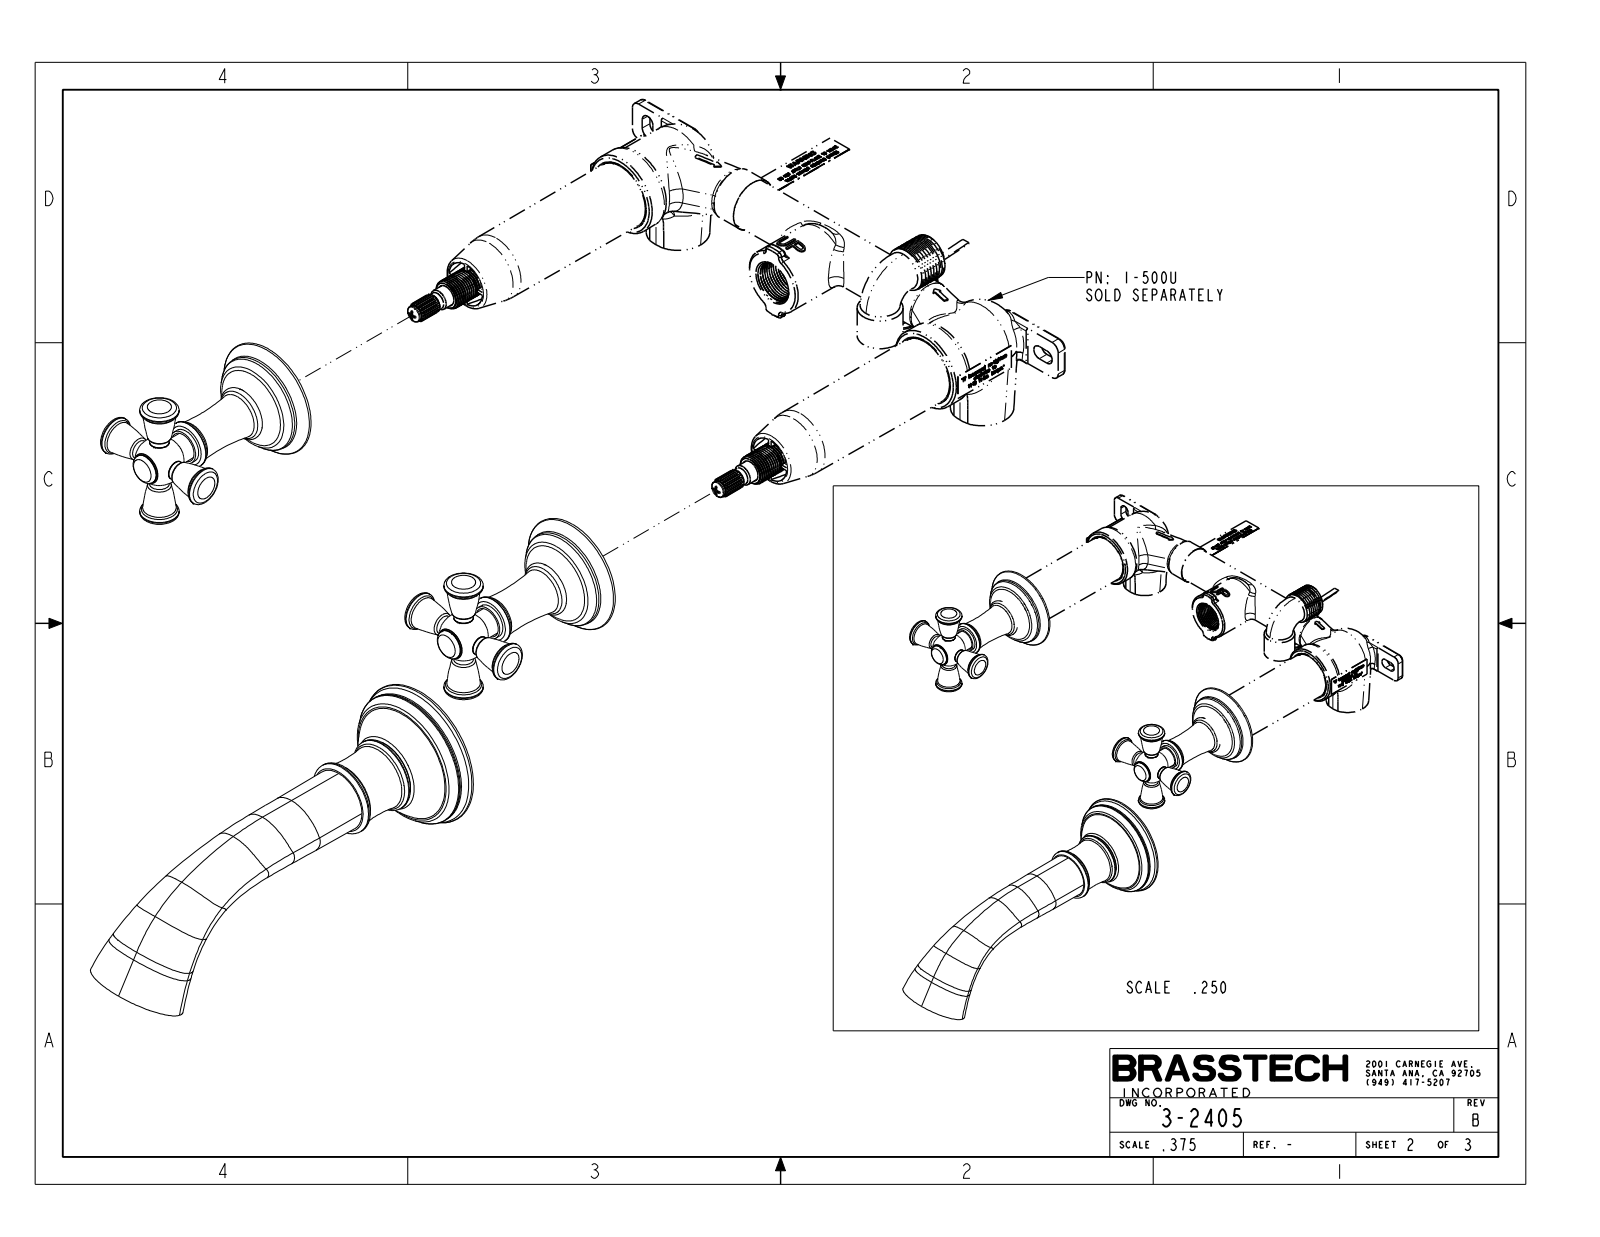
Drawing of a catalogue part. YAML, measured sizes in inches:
part_name: "3-2405_SW0001"
step_written_by: "CREO PARAMETRIC BY PTC INC, 2018400 (AUTOMOTIVE_DESIGN)"
units: inches
bodies: {solids: 3, faces: 337, planar: 19, cylindrical: 52, other: 266}
overall_size: [10.403, 9.052, 7.825]
volume: 19.31
surface_area: 90.41
round_bosses_or_shafts:
  - {diameter: 0.72, count: 3}
  - {diameter: 0.36, count: 3}
  - {diameter: 0.9, count: 2}
  - {diameter: 0.649, count: 2}
  - {diameter: 0.56, count: 2}
  - {diameter: 0.517, count: 2}
  - {diameter: 1.4, count: 1}
face_to_face_distances: [2.14, 2.22, 0.08, 0.481, 1.659, 1.739, 0.925, 0.444, 1.215, 1.295]
